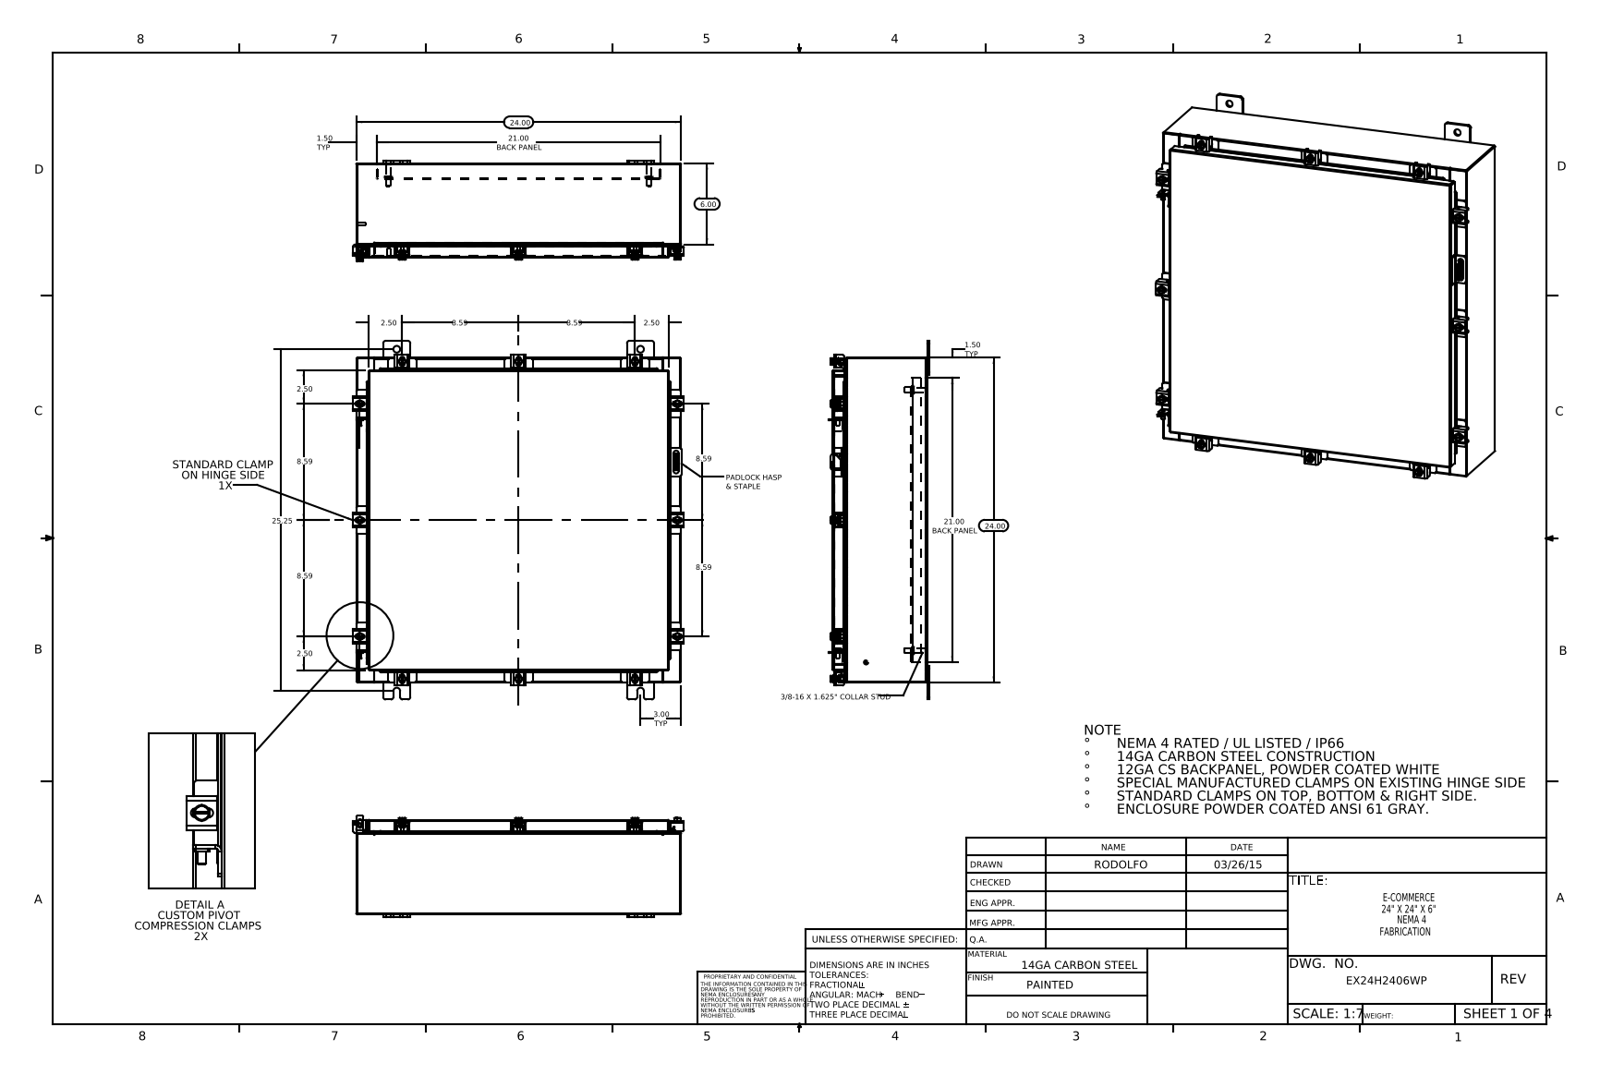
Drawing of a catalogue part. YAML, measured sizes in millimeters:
part_name: "EX24H2406WP Padlock Hasp; N-WMT04X30402202210-00 22104005_DEFAULT; 30X10 Clamp Bracket2; Clamp Top_RTP31 (+8 more)"
step_written_by: "SolidWorks 2014 (CONFIG_CONTROL_DESIGN)"
units: millimeters
bodies: {solids: 81, faces: 2018, planar: 1075, cylindrical: 783, other: 160}
overall_size: [673.1, 620.3, 189.3]
volume: 3313000
surface_area: 3241000
round_holes:
  - {diameter: 5.4, count: 12}
  - {diameter: 6.6, count: 12}
  - {diameter: 12.7, count: 8}
  - {diameter: 3.2, count: 1}
  - {diameter: 6.4, count: 1}
round_bosses_or_shafts:
  - {diameter: 12.7, count: 12}
  - {diameter: 6.4, count: 12}
  - {diameter: 10.1, count: 10}
  - {diameter: 15.9, count: 4}
  - {diameter: 9.5, count: 4}
  - {diameter: 8.4, count: 4}
  - {diameter: 8, count: 2}
  - {diameter: 6, count: 2}
partial_cylinders:
  - {radius: 1.5, count: 54}
  - {radius: 0.3, count: 24}
  - {radius: 3.6, count: 24}
  - {radius: 4.8, count: 24}
  - {radius: 2.2, count: 22}
  - {radius: 3, count: 22}
  - {radius: 2.3, count: 18}
  - {radius: 1.3, count: 17}
face_to_face_distances: [1.9, 175.3, 607.7, 177.2, 173.4, 2.6, 25.4, 27.3, 148, 149.9]
hole_center_spacings: [218.3, 308.3, 522.2, 595.9, 634.4, 59.4, 465.8, 543]
